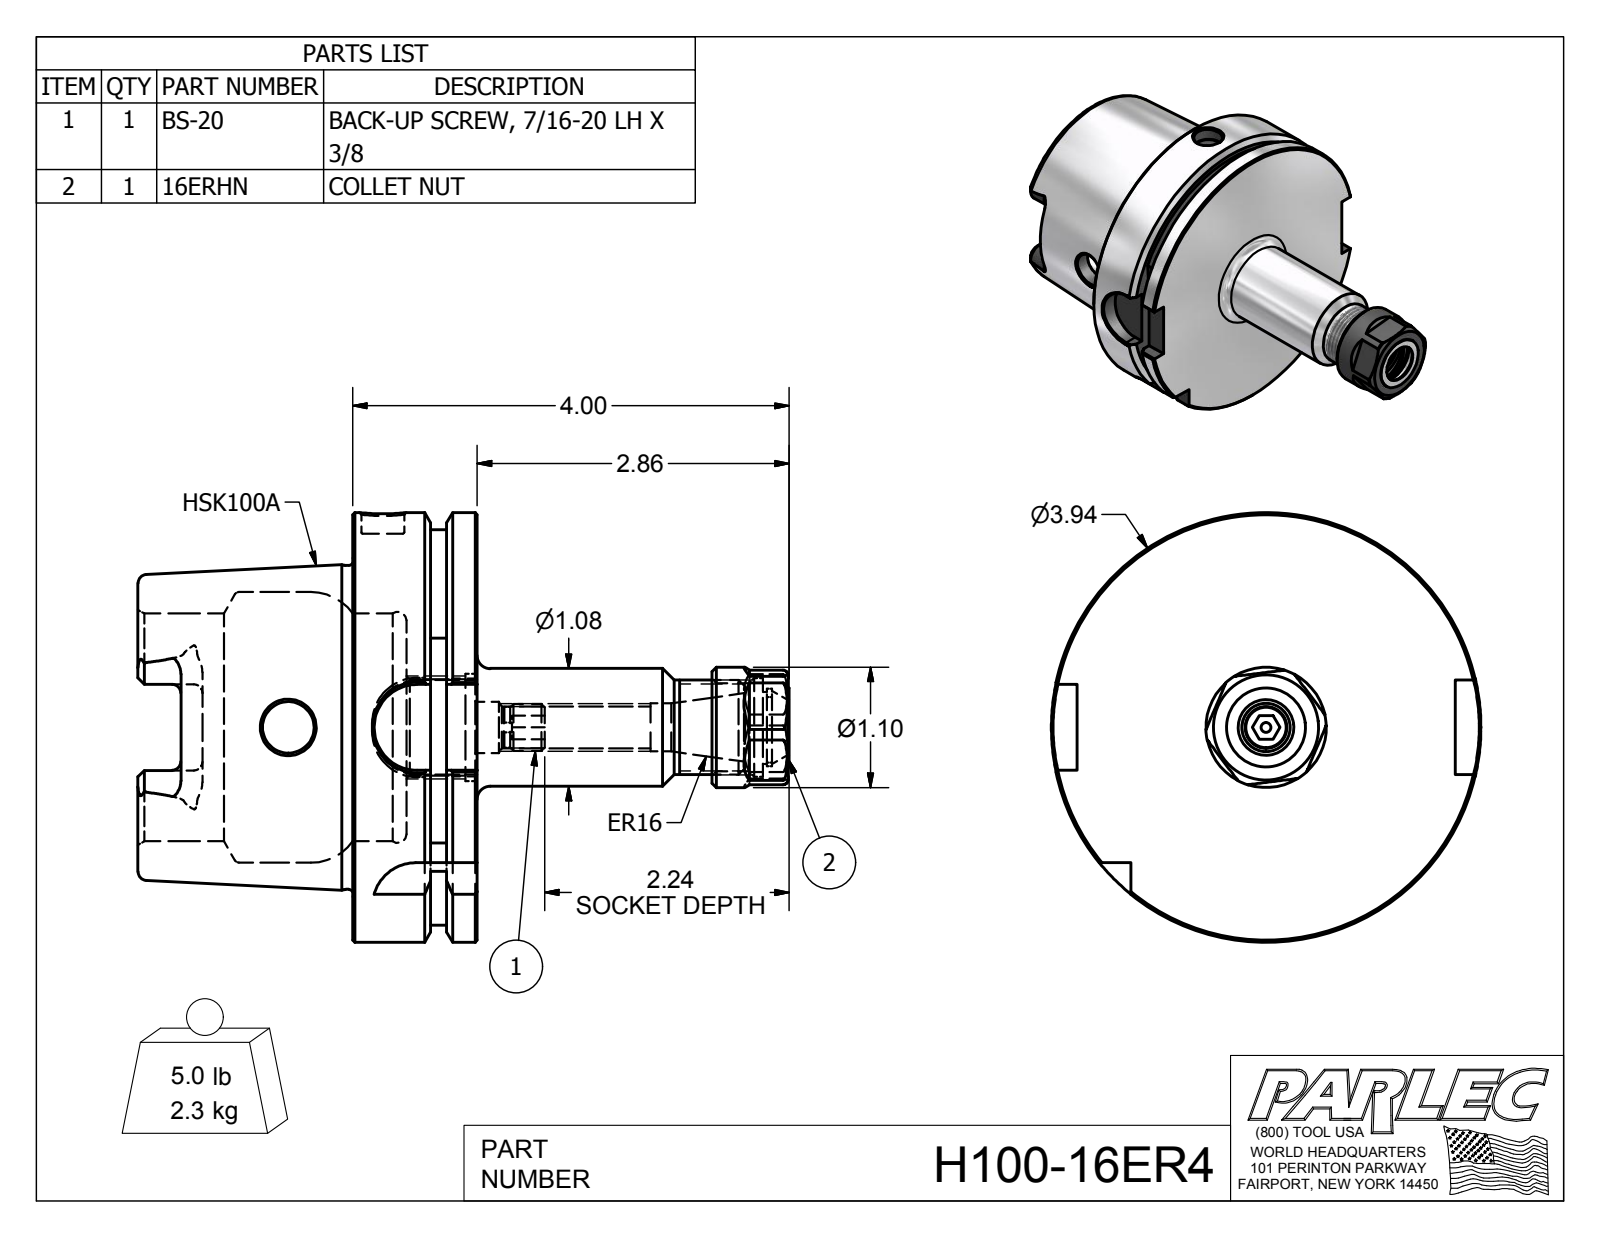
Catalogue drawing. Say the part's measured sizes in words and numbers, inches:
The part is named "H100-16ER4; H100-16ER4-1; BS-20; 16ERHN". Its 3-D file was written by "Autodesk Inventor 2012 (AUTOMOTIVE_DESIGN)". It is 3 solids with 181 faces: 71 planar, 46 cylindrical and 64 other. Overall it measures 5.969 by 3.937 by 3.937 inches. Its volume is 17.47 cubic inches and its surface area 94.52 square inches. Round holes: 2 of diameter 0.472, 1 of diameter 0.09, 1 of diameter 0.383, 1 of diameter 0.394, 1 of diameter 0.44, 1 of diameter 0.472, 1 of diameter 0.508, 1 of diameter 0.661, 1 of diameter 0.807, 1 of diameter 0.881, 1 of diameter 0.906, 1 of diameter 0.985. Round bosses or shafts: 1 of diameter 3.937, 1 of diameter 2.967, 1 of diameter 1.102, 1 of diameter 1.08, 1 of diameter 0.866, 1 of diameter 0.724, 1 of diameter 0.432, 1 of diameter 0.373. Partial cylindrical surfaces (rounded edges, fillets, slot ends): 6 of radius 0.079, 4 of radius 0.192, 4 of radius 0.394, 1 of radius 0.354, 1 of radius 1.811. The main face-to-face distances are 1.142, 0.492, 0.65, 1.969, 2.461, 3.11, 2.83, 0.861, 0.369, 0.28. The hole center spacings are 0.051.
